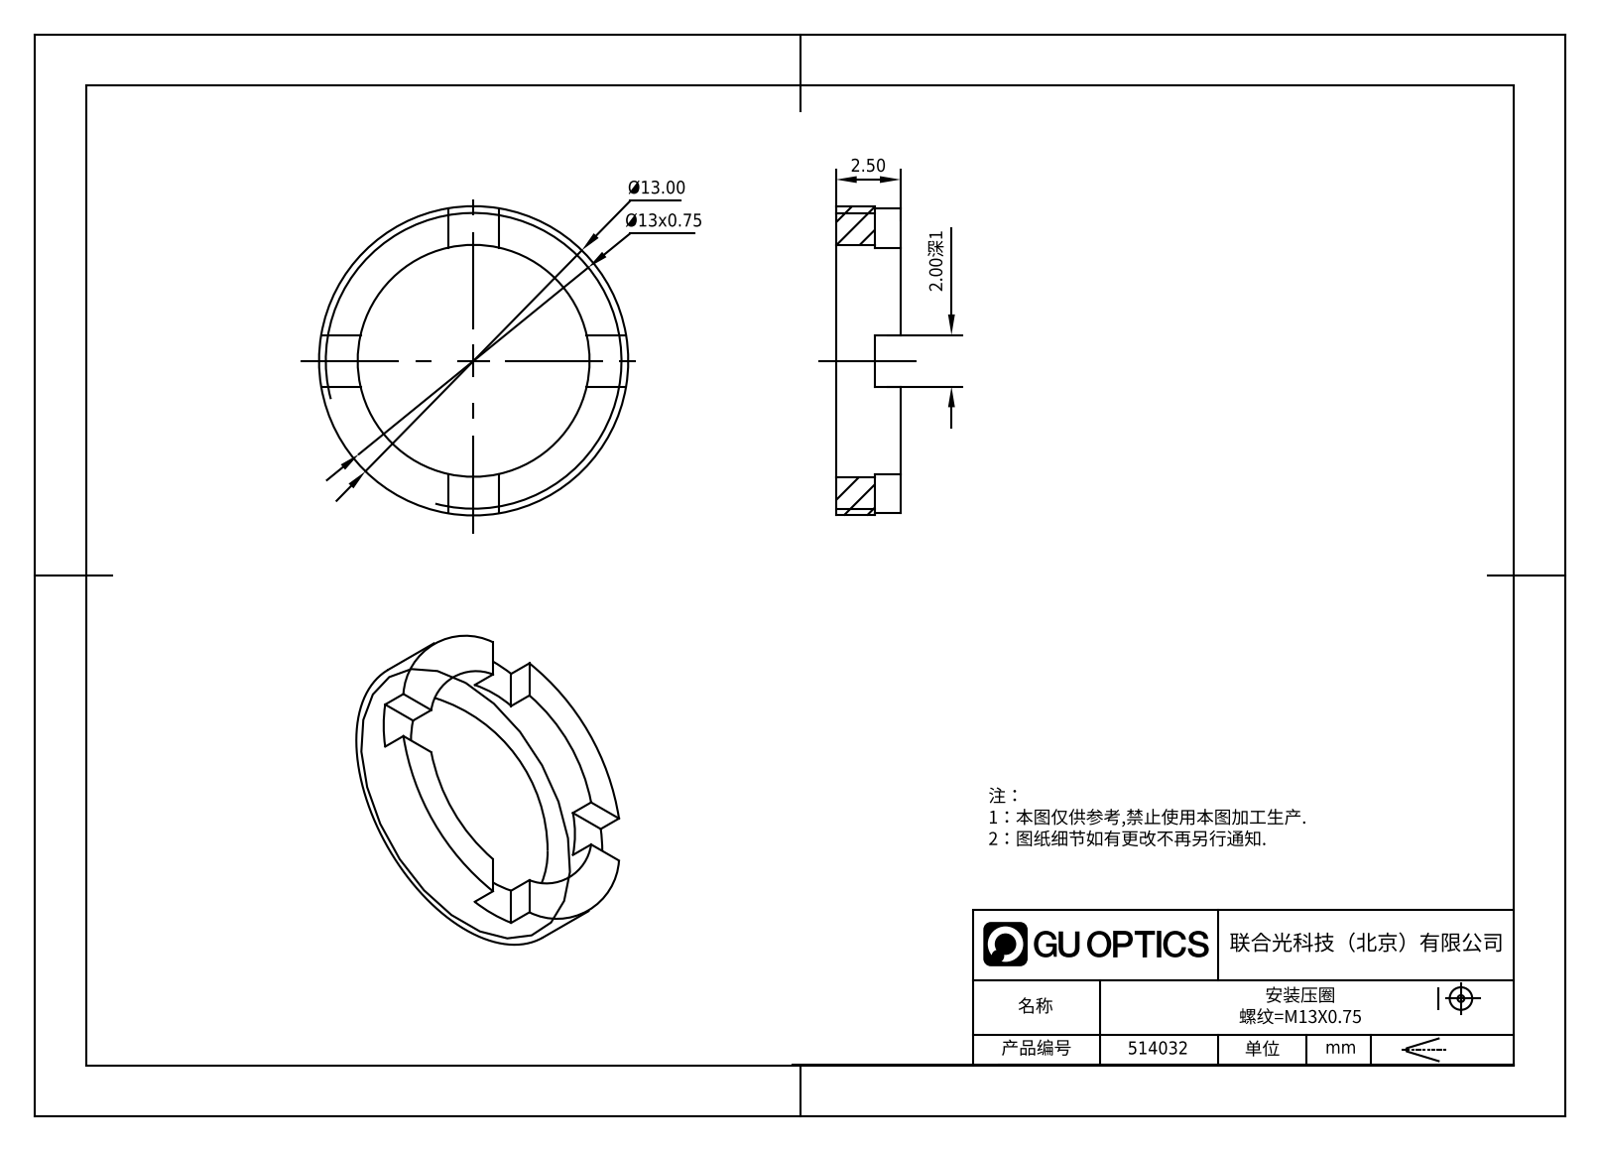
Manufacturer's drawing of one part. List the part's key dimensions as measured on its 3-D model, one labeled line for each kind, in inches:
Part name (STEP PRODUCT): 514032
STEP written by: SolidWorks 2020 (CONFIG_CONTROL_DESIGN)
Units: inches
Bodies: 1 solid, 21 faces (17 planar, 4 cylindrical, 0 other)
Overall size (bounding box): 0.512 × 0.512 × 0.098
Volume: 0.008 in³ · Surface area: 0.442 in²
Round holes (diameter × count): ⌀0.394 ×1
Round bosses / shafts (diameter × count): ⌀0.512 ×1
Main face-to-face distances: 0.098, 0.059, 0.039, 0.079
